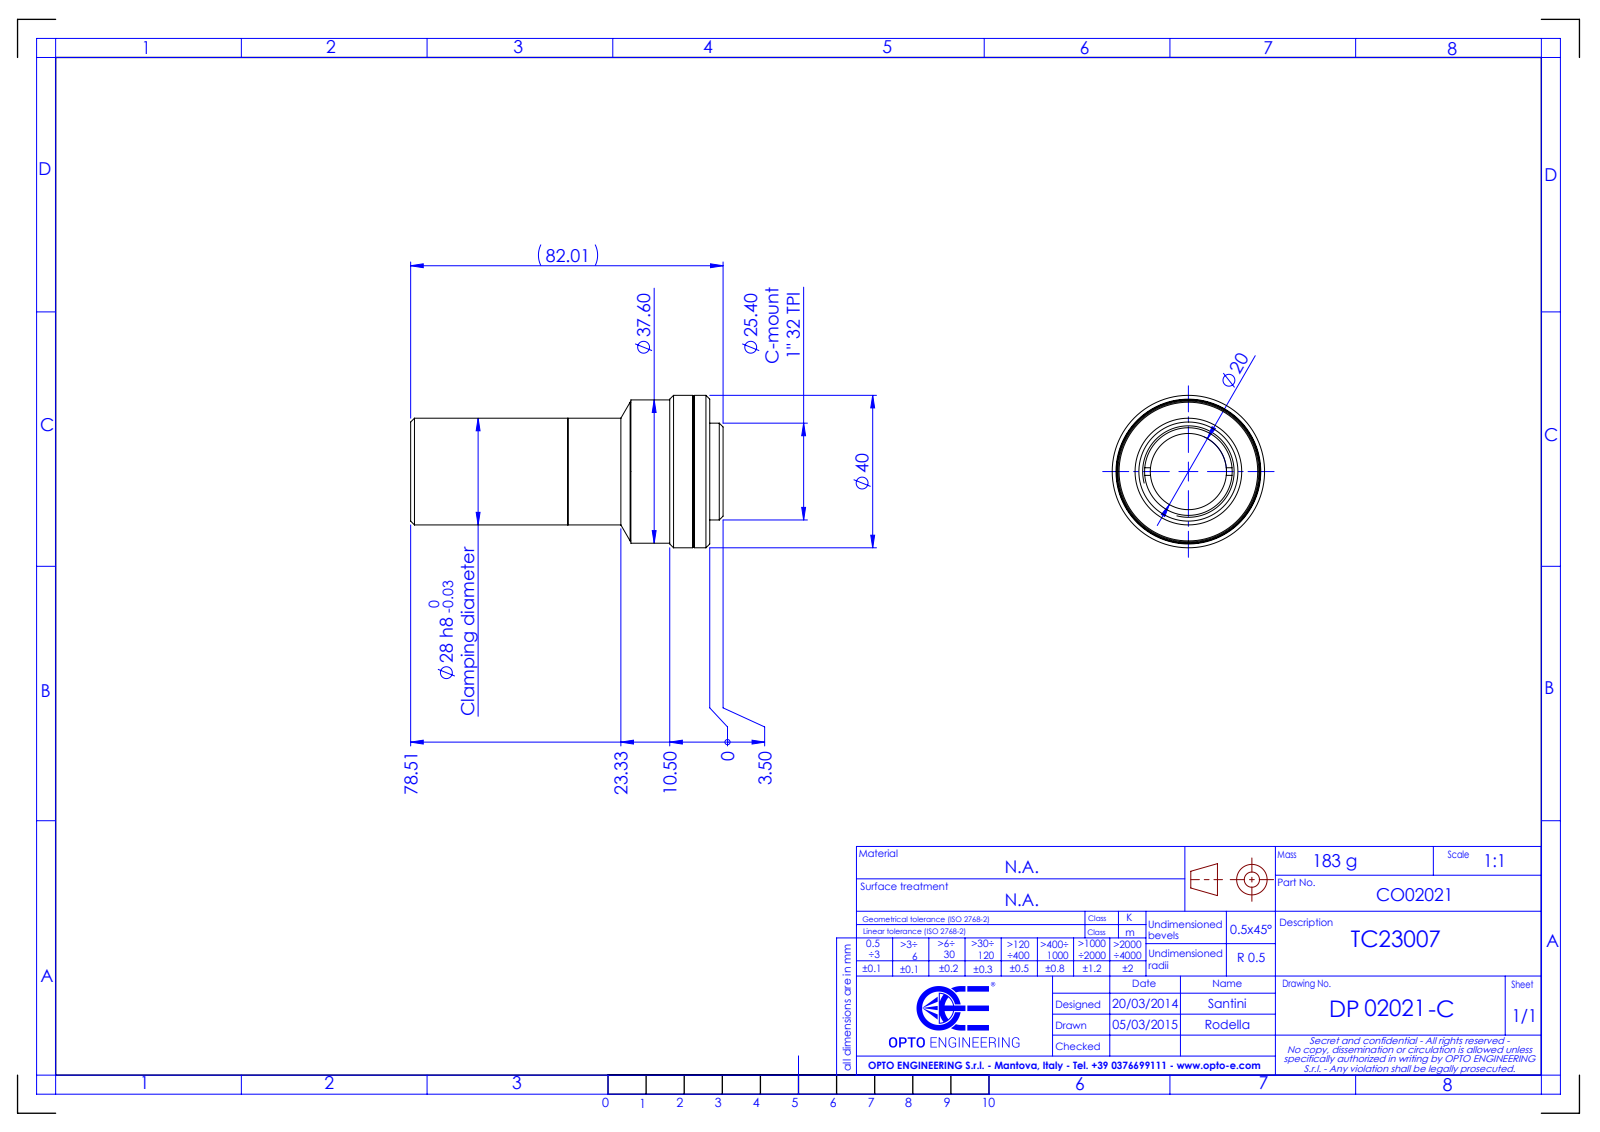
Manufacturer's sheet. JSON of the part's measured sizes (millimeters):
{"part_name": "DP02021_TC23007", "step_written_by": "SolidWorks 2021 (CONFIG_CONTROL_DESIGN)", "units": "millimeters", "bodies": {"solids": 0, "faces": 77, "planar": 29, "cylindrical": 30, "other": 18}, "overall_size": [82.01, 40, 40], "round_holes": [[14, 1], [19, 1], [20, 1], [22.5, 1], [23, 1]], "round_bosses_or_shafts": [[40, 1], [39.8, 1], [37.6, 1], [36.4, 1], [28, 1], [25.4, 1]], "face_to_face_distances": [0.4, 4.4, 4, 0.5, 4.5, 32.73, 32.83, 33.23, 37.23, 39.51]}
